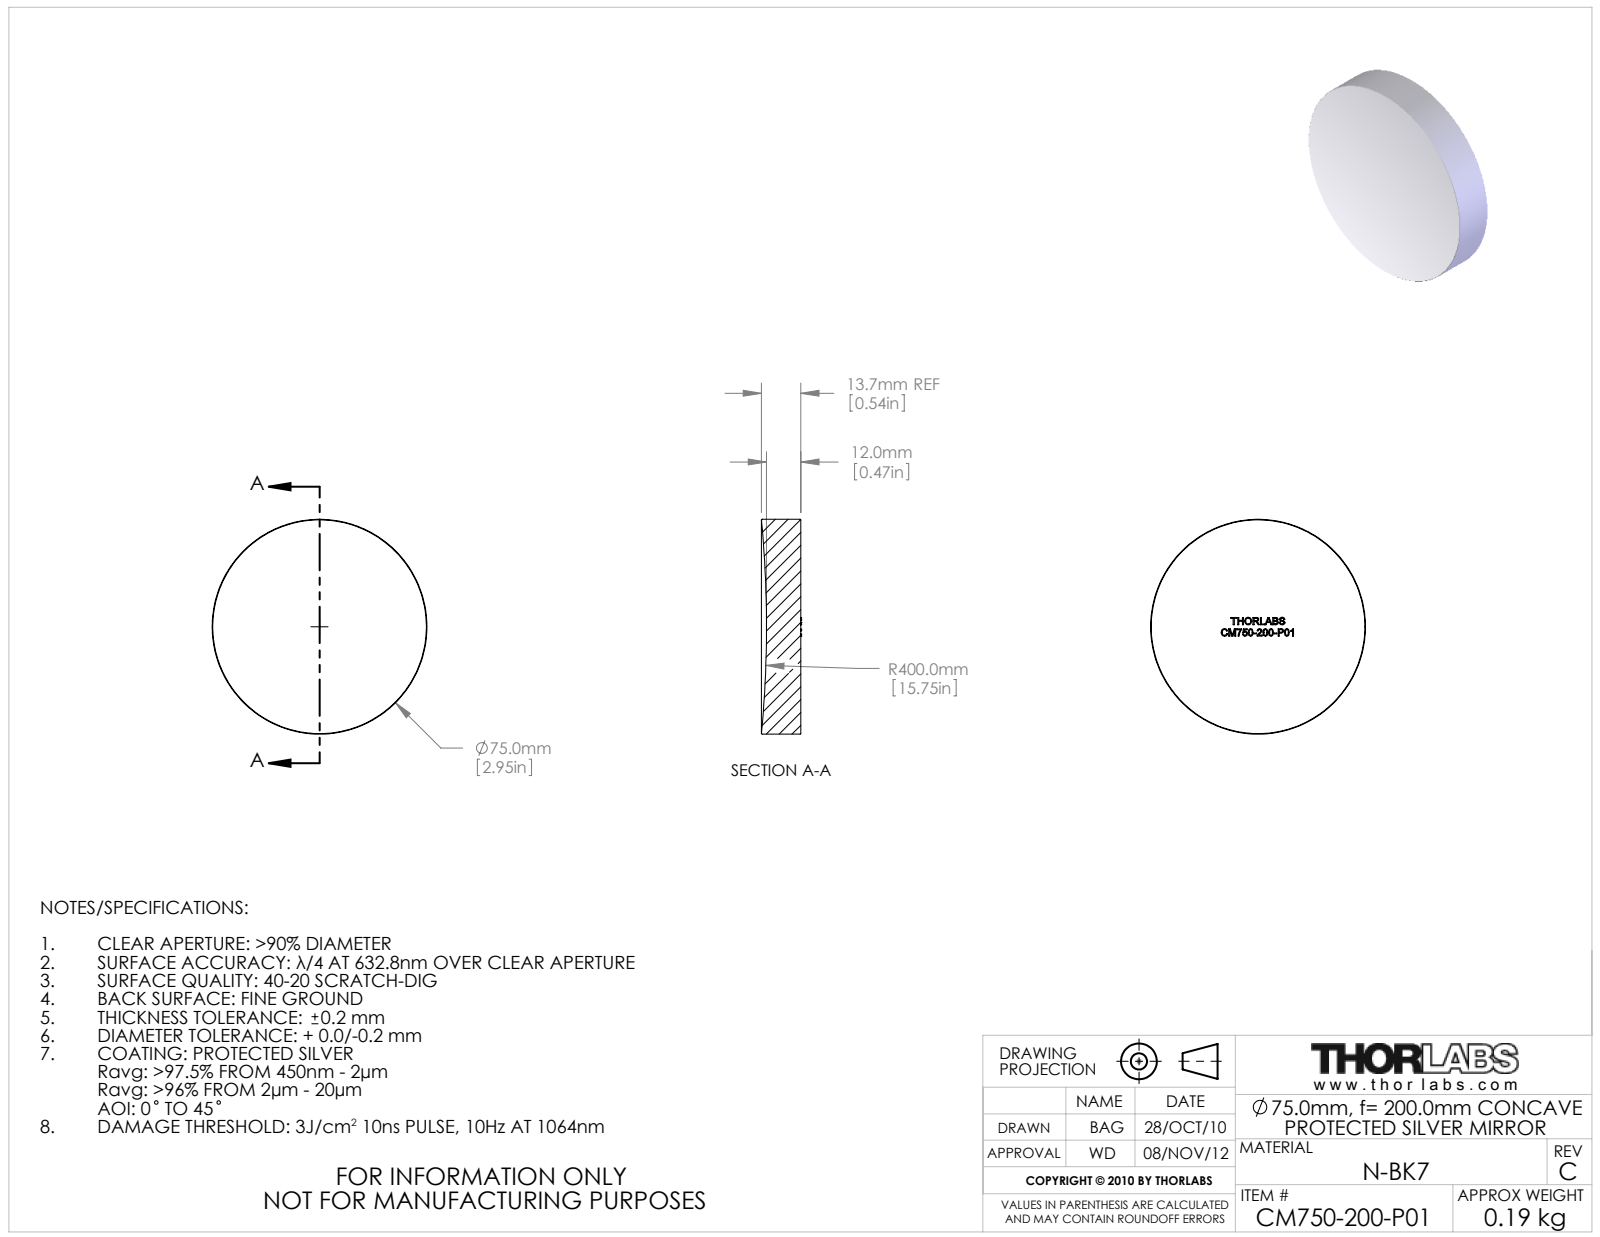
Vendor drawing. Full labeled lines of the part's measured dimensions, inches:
Part name (STEP PRODUCT): 17577-E0W
STEP written by: SolidWorks 2009 (AUTOMOTIVE_DESIGN)
Units: inches
Bodies: 1 solid, 272 faces (143 planar, 2 cylindrical, 127 other)
Overall size (bounding box): 2.953 × 2.953 × 0.541
Volume: 3.472 in³ · Surface area: 18.65 in²
Round bosses / shafts (diameter × count): ⌀2.953 ×1
Main face-to-face distances: 0.101, 0.014, 0.015, 0.089, 0.058, 0.156, 0.258, 0.244, 0.187, 0.013
